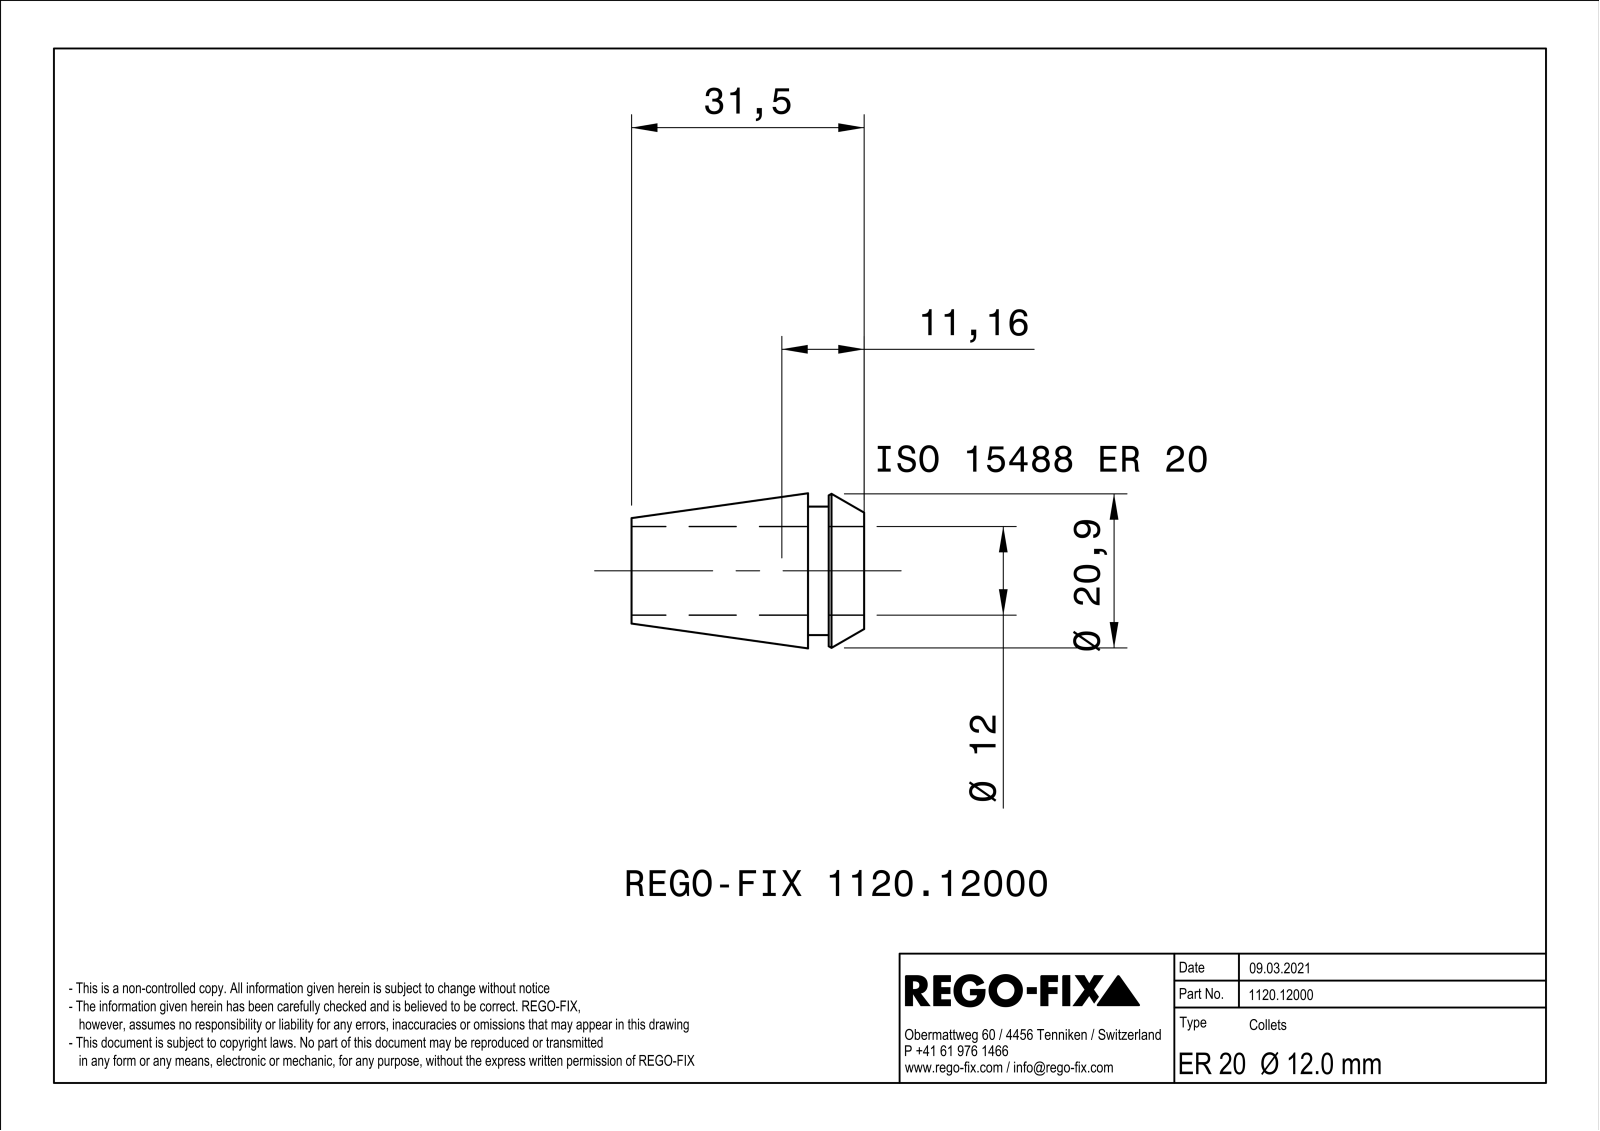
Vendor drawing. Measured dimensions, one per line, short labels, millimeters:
name: NOCUT
written by: SIEMENS PLM Software Solid Edge ST10 (AUTOMOTIVE_DESIGN)
unit: mm
bodies: 1 solid, 177 faces (88 planar, 9 cylindrical, 80 other)
size: 31.5 × 20.99 × 20.99
volume: 3 544 mm³; area: 5 324 mm²
holes: 1× ⌀12
bosses: 1× ⌀17.4
face distances: 0.6, 2.8, 4.8, 7.6, 31.5, 26.7, 23.9, 5.5, 0.7, 2.1
